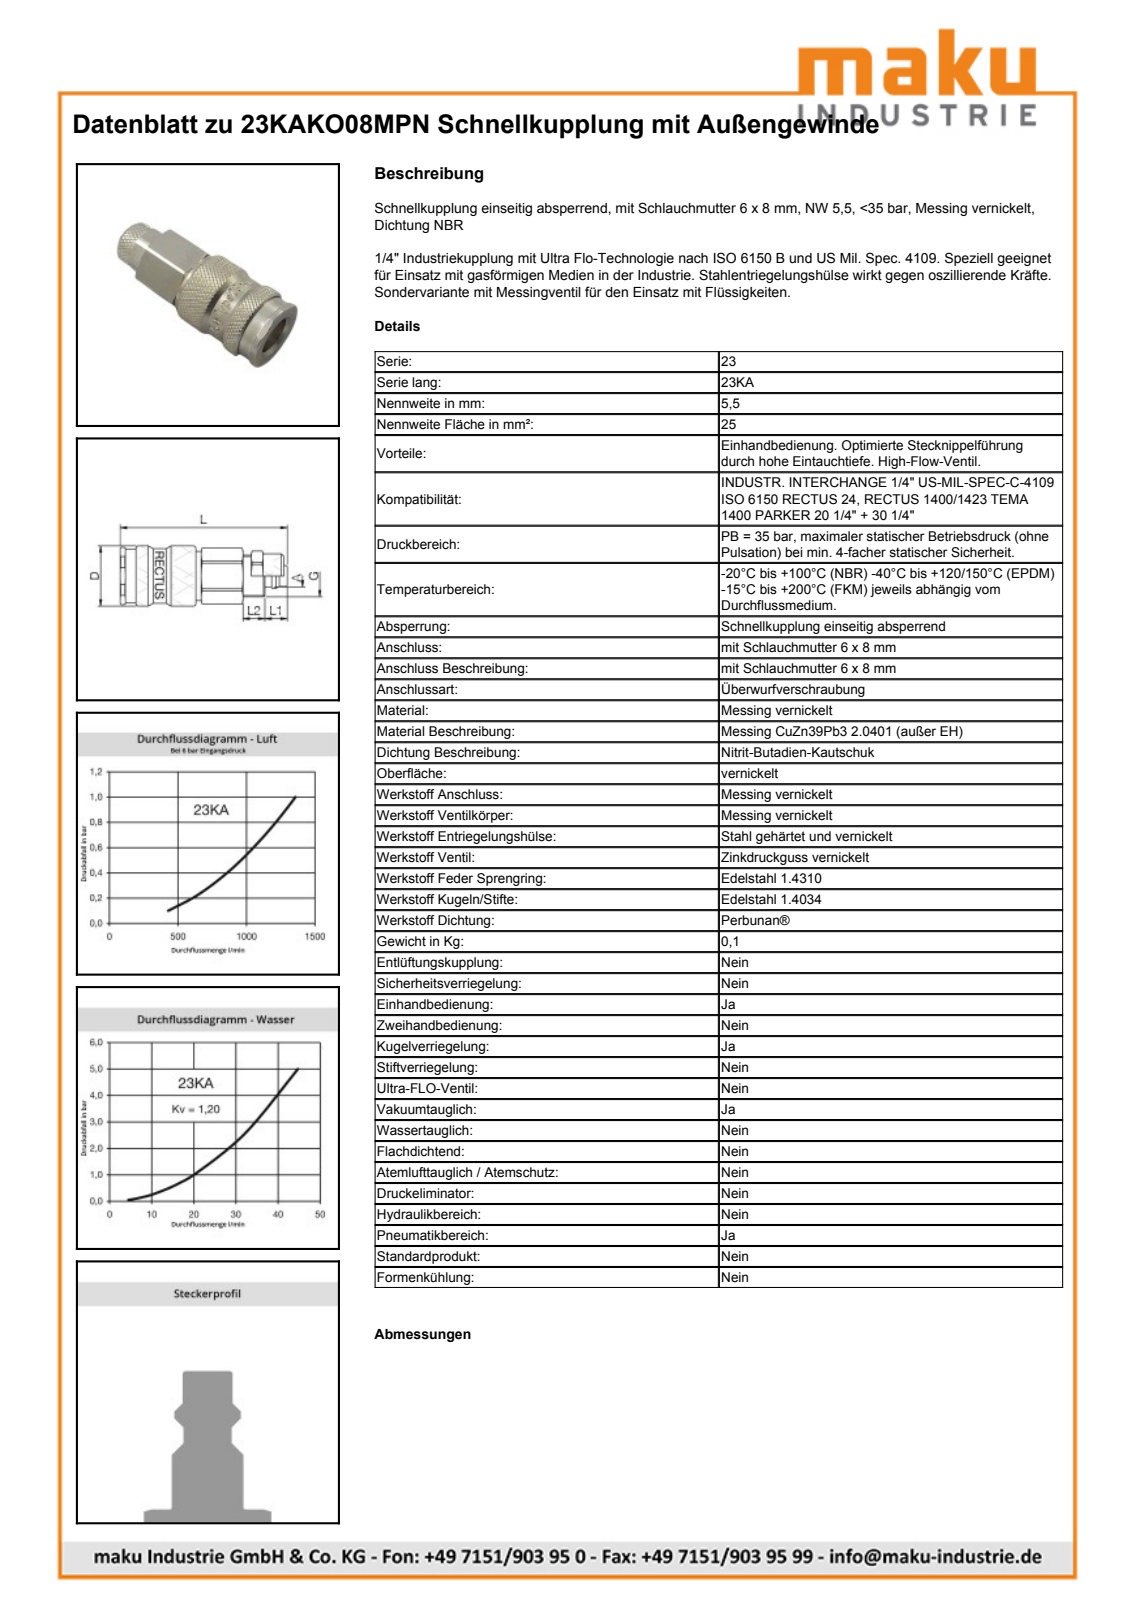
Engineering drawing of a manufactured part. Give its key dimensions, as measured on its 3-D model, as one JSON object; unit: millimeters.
{"part_name": "23KAKO08MPN", "step_written_by": "Autodesk Inventor 2020 (AUTOMOTIVE_DESIGN)", "units": "millimeters", "bodies": {"solids": 2, "faces": 557, "planar": 175, "cylindrical": 71, "other": 311}, "overall_size": [60.1, 23.15, 23.15], "volume_mm3": 17408, "surface_area_mm2": 7996, "round_holes": [[11.15, 1], [17.25, 1], [19.35, 1]], "round_bosses_or_shafts": [[23.15, 1], [21, 1], [20.8, 1], [20.6, 1], [18.95, 1], [16.5, 1], [14, 1], [12, 1]], "partial_cylinders_radius": [[7.75, 1], [10.7, 1], [11, 1]], "face_to_face_distances": [19, 46.85, 1, 14, 58.85, 12, 20, 24.1, 22.75, 34.75]}
